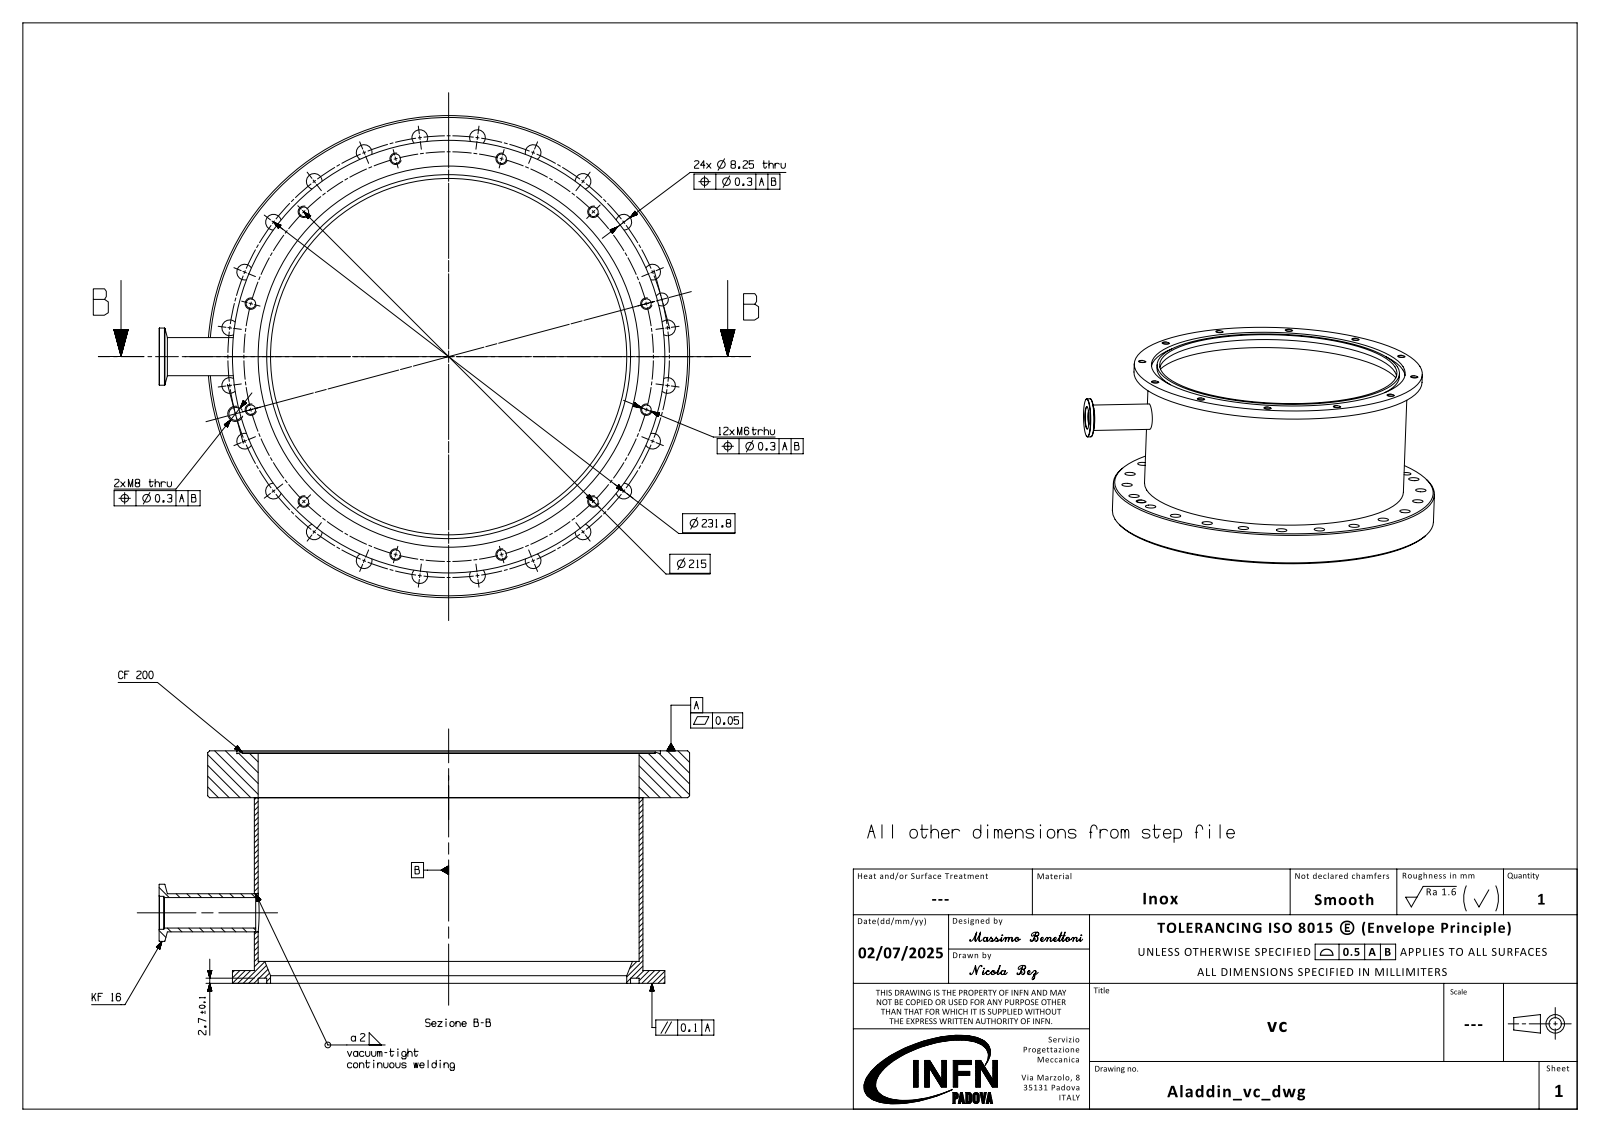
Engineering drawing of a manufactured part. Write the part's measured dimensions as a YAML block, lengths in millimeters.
part_name: "vc_objects"
step_written_by: "SIEMENS PLM Software NX2306.9102 (AUTOMOTIVE_DESIGN)"
units: millimeters
bodies: {solids: 3, faces: 73, planar: 12, cylindrical: 51, other: 10}
overall_size: [278.5, 253, 122]
volume: 632586
surface_area: 245358
round_holes:
  - {diameter: 8.25, count: 24}
  - {diameter: 5, count: 12}
  - {diameter: 6.8, count: 2}
  - {diameter: 16, count: 1}
  - {diameter: 17.3, count: 1}
  - {diameter: 187, count: 1}
  - {diameter: 200, count: 1}
  - {diameter: 222.3, count: 1}
round_bosses_or_shafts:
  - {diameter: 253, count: 1}
  - {diameter: 227, count: 1}
  - {diameter: 204, count: 1}
  - {diameter: 191, count: 1}
  - {diameter: 30, count: 1}
  - {diameter: 20, count: 1}
face_to_face_distances: [97.4, 24.6, 122, 115.3, 90.7, 6.7, 1.4, 23.2, 113.9, 120.6]
hole_center_spacings: [115.9, 223.9, 163.9, 183.9, 200.74, 214.15, 88.7, 59.99]
